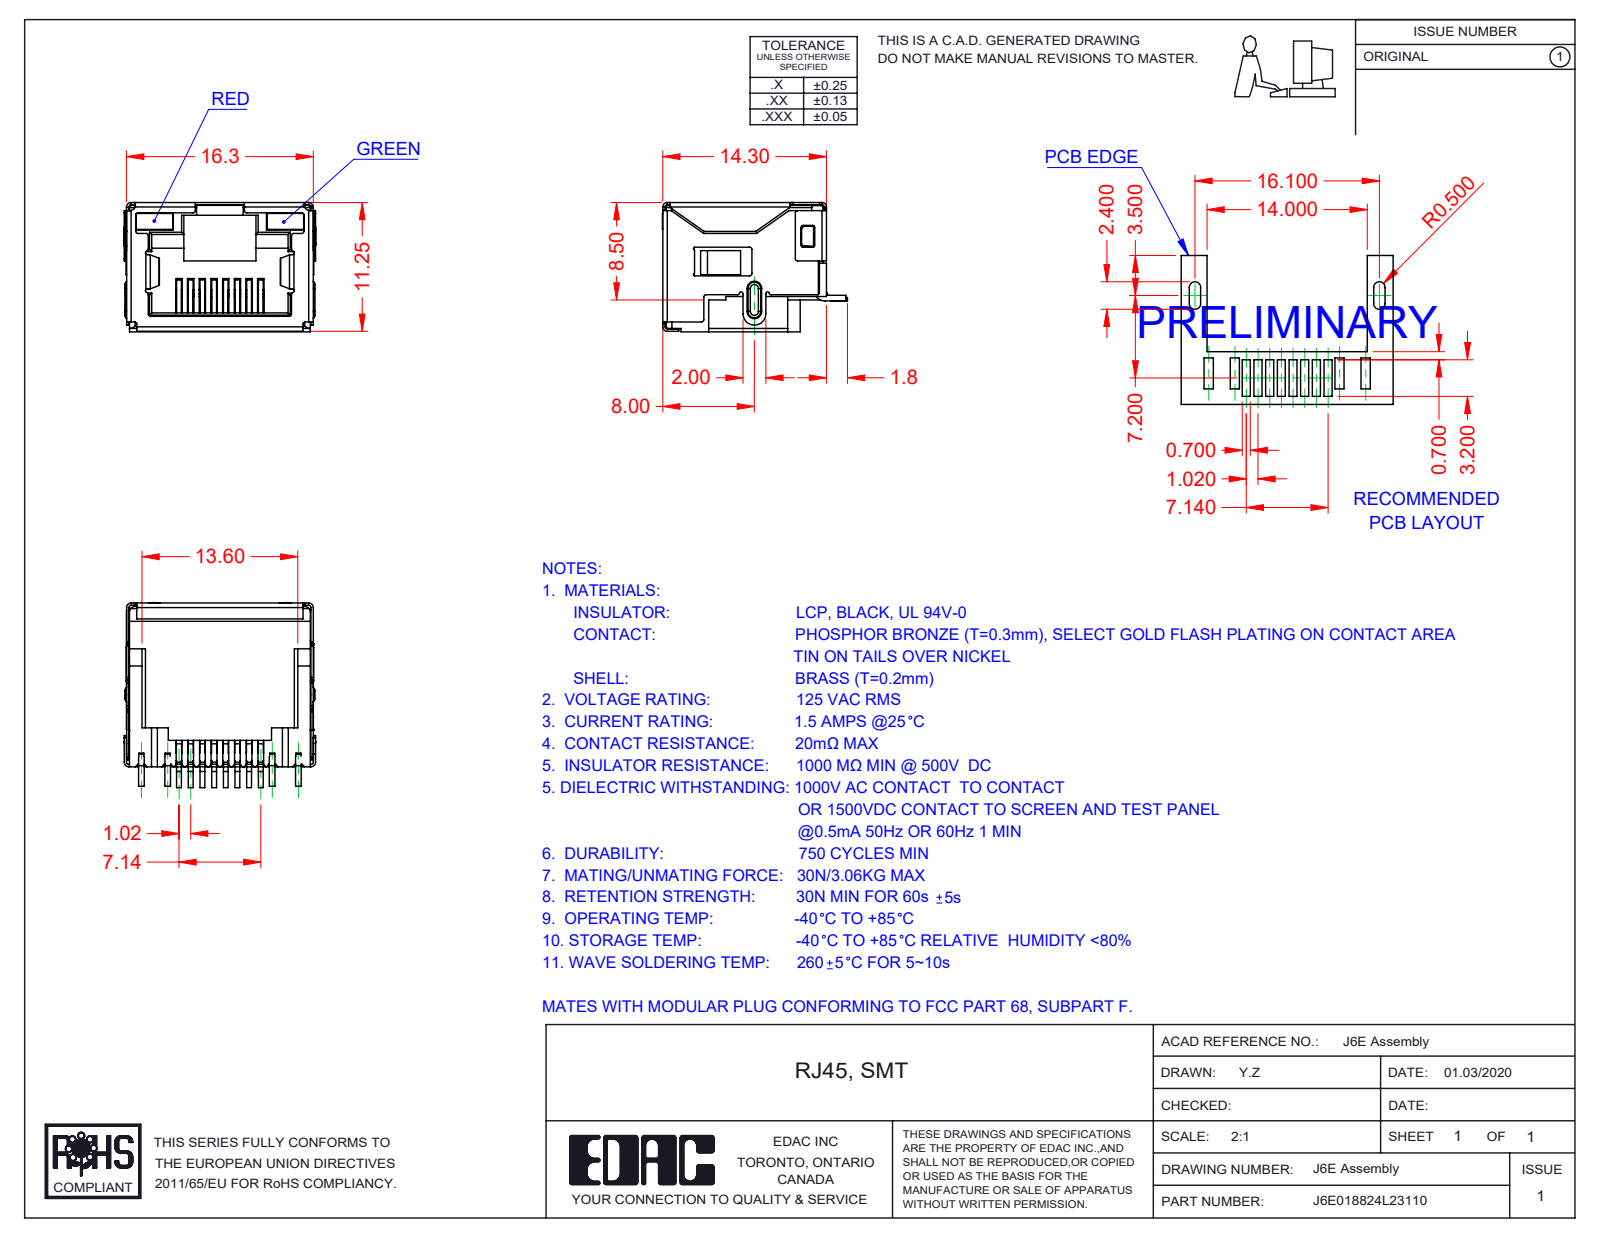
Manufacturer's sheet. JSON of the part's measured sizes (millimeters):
{"part_name": "6E LED LH_2-Red; 6E Shield_LED; 6E LED RH_3-Green; 6E Contacts (+2 more)", "step_written_by": "SolidWorks 2016 (CONFIG_CONTROL_DESIGN)", "units": "millimeters", "bodies": {"solids": 12, "faces": 1496, "planar": 1099, "cylindrical": 347, "other": 50}, "overall_size": [16.75, 16.15, 11.3], "volume_mm3": 1109, "surface_area_mm2": 4045, "partial_cylinders_radius": [[0.2, 82], [0.25, 17], [0.4, 13], [0.5, 13], [0.1, 10], [0.15, 7], [0.3, 4], [1, 3]], "face_to_face_distances": [11.05, 16.05, 16.1, 15.85, 11.1, 11.3, 2.4, 0.7, 9.85, 0.49]}
